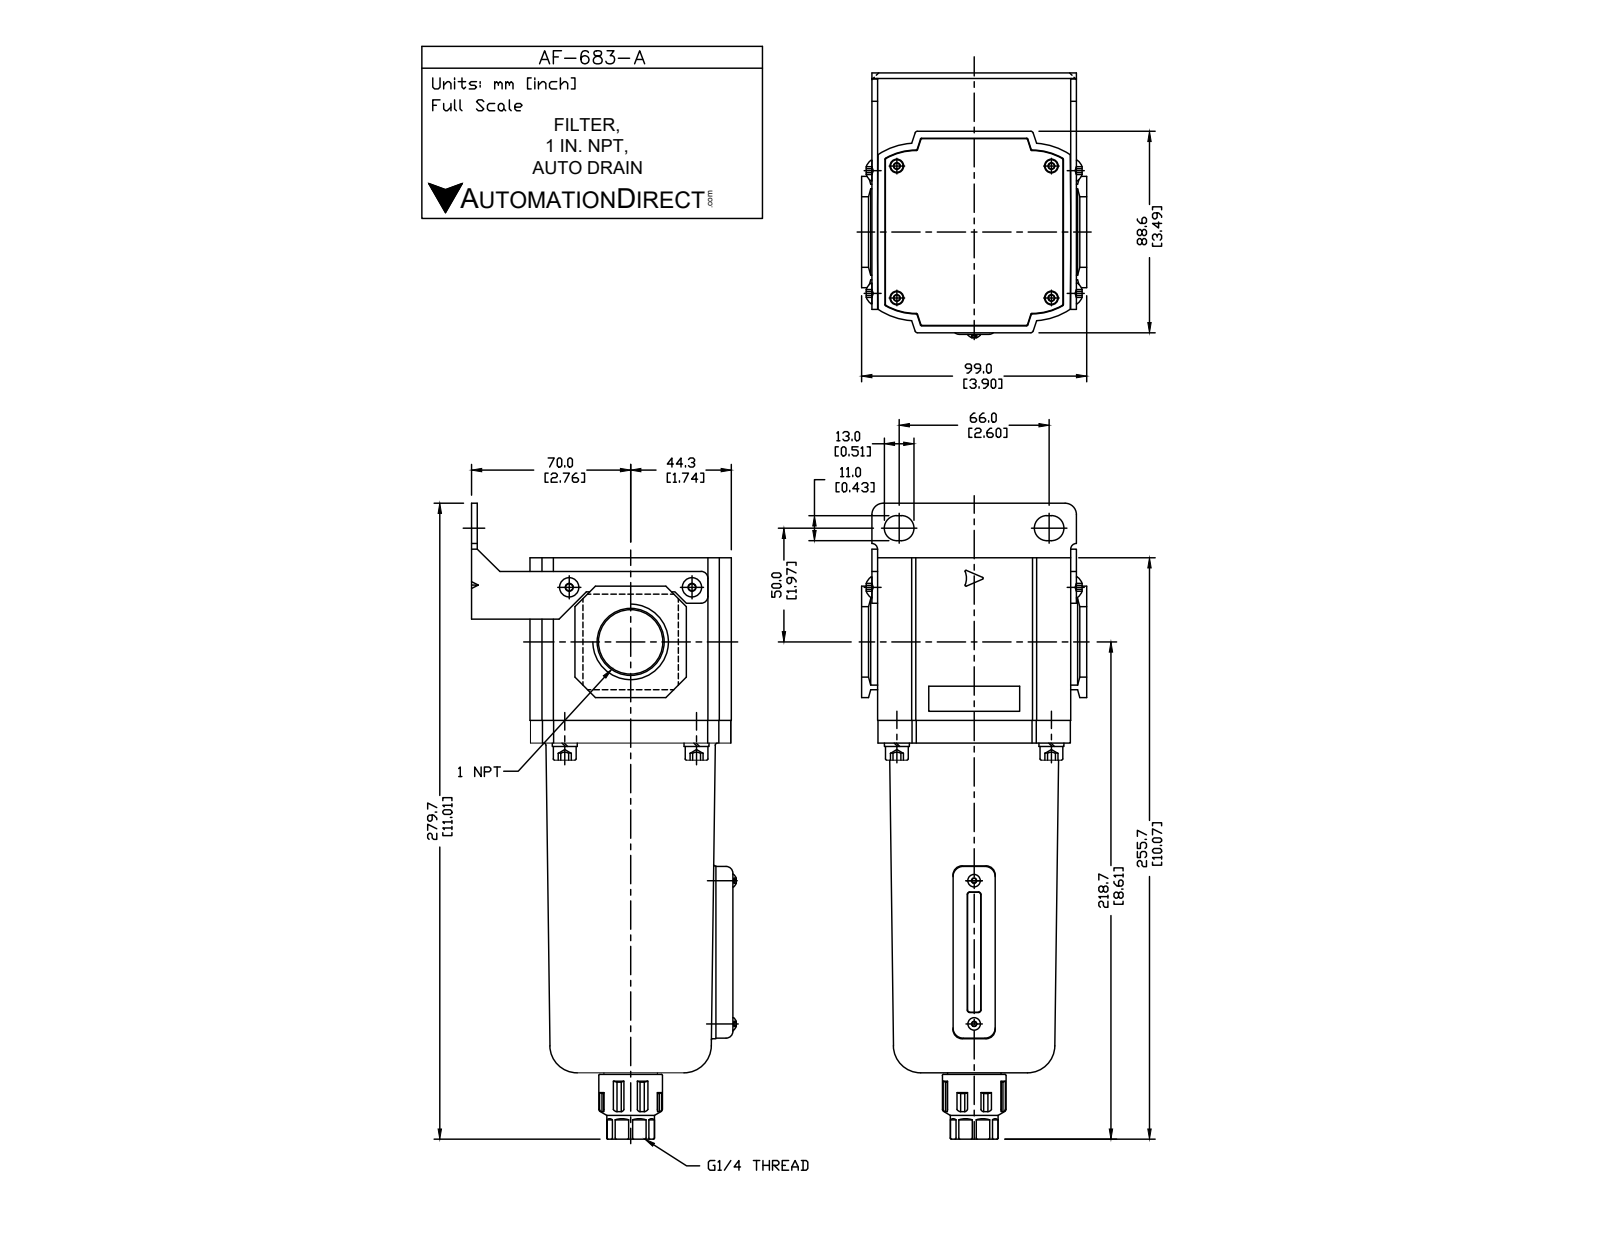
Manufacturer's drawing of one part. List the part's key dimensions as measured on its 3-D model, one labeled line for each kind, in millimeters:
Part name (STEP PRODUCT): AF-683-A
STEP written by: SolidWorks 2015 (CONFIG_CONTROL_DESIGN)
Units: millimetres
Bodies: 8 solids, 384 faces (233 planar, 88 cylindrical, 63 other)
Overall size (bounding box): 280 × 116.49 × 99
Volume: 1 224 000 mm³ · Surface area: 120 794 mm²
Round holes (diameter × count): ⌀5.5 ×2, ⌀11.45 ×1, ⌀28.98 ×1
Round bosses / shafts (diameter × count): ⌀10 ×4, ⌀74.5 ×1, ⌀28 ×1, ⌀21 ×1
Partial cylindrical surfaces — rounded edges, fillets, slot ends (radius × count): R3 ×10, R9.5 ×8, R0.5 ×6, R2 ×5, R0.3 ×4, R1 ×4, R5.5 ×4, R29.7 ×4
Main face-to-face distances: 2.5, 71.5, 85, 25.7, 23.2, 114.3, 111.8, 88.6, 87.5, 92
Hole centre spacings: 36.12, 54
